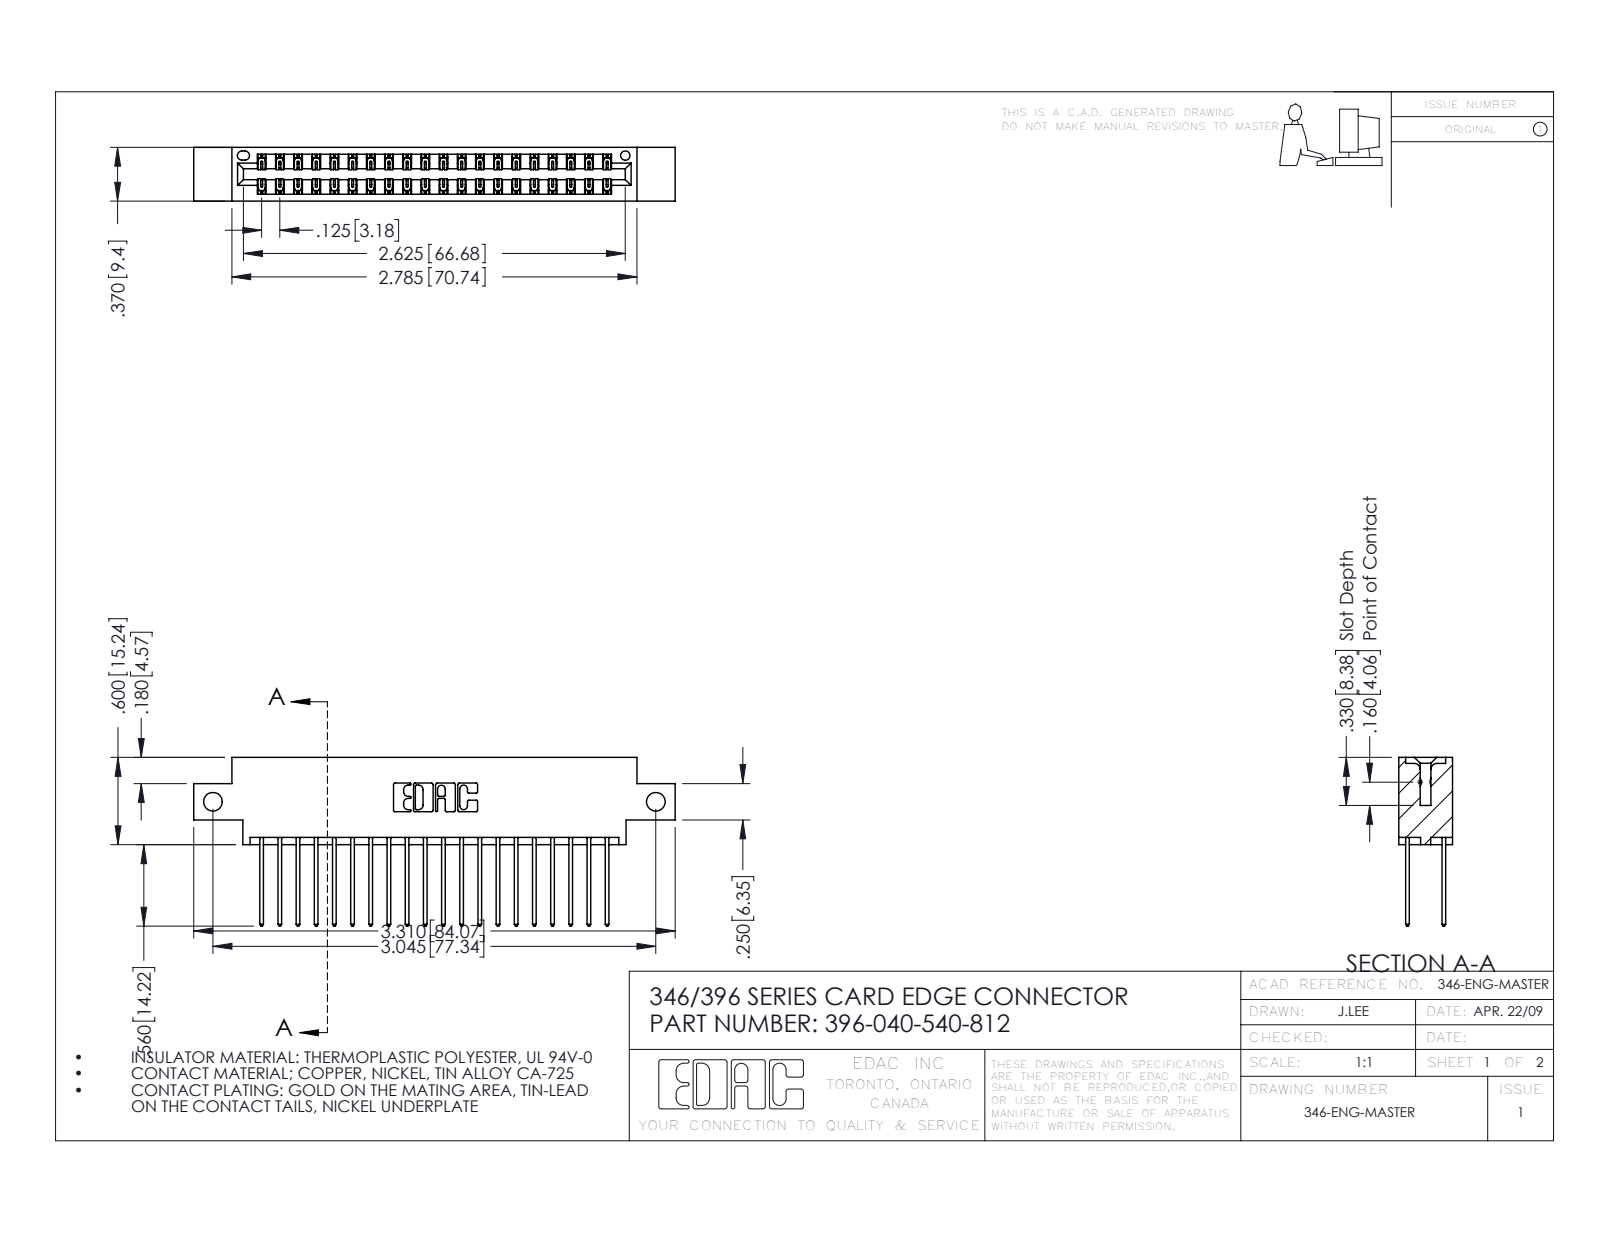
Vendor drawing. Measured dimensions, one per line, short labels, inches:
name: 396-040-540-812; 345-292-001_345-293-140; 346 Part_0.170 Offset - Side Mount
written by: SolidWorks 2016 (CONFIG_CONTROL_DESIGN)
unit: in
bodies: 41 solids, 2206 faces (1480 planar, 726 cylindrical, 0 other)
size: 3.31 × 1.16 × 0.37
volume: 0.484 in³; area: 17.55 in²
holes: 2× ⌀0.128, 1× ⌀0.064
rounds: 60× R0.006, 40× R0.01, 22× R0.01, 6× R0.007, 6× R0.031, 3× R0.026, 2× R0.014, 2× R0.022
face distances: 0.048, 0.322, 0.25, 0.37, 0.072, 0.298, 0.025, 0.275, 0.148, 0.222
hole spacings: 3.045
